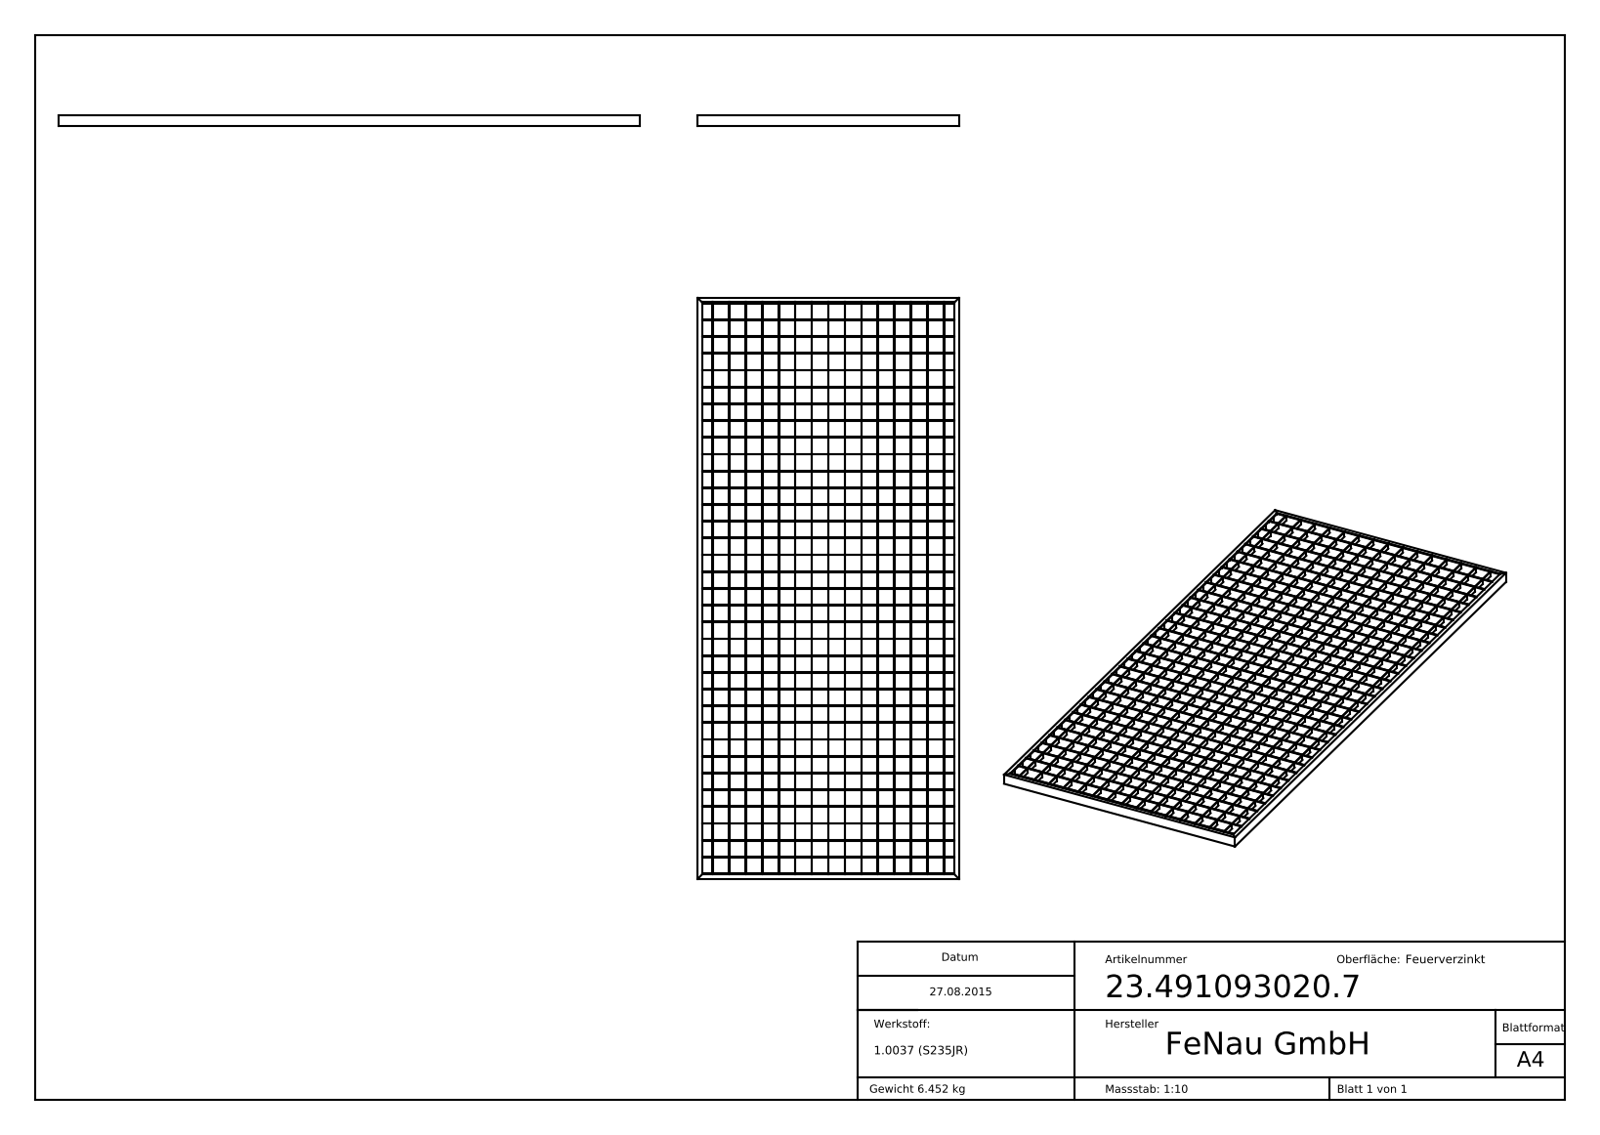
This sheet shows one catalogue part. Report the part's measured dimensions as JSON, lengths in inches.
{"part_name": "23-491093020-7", "step_written_by": "SolidWorks 2015 (CONFIG_CONTROL_DESIGN)", "units": "inches", "bodies": {"solids": 1, "faces": 1980, "planar": 1980, "cylindrical": 0, "other": 0}, "overall_size": [42.913, 19.291, 0.787], "volume_in3": 50.48, "surface_area_in2": 1910, "face_to_face_distances": [2.48, 1.24, 3.72, 1.22, 4.961, 6.201, 7.441, 8.681, 2.441, 9.921]}
